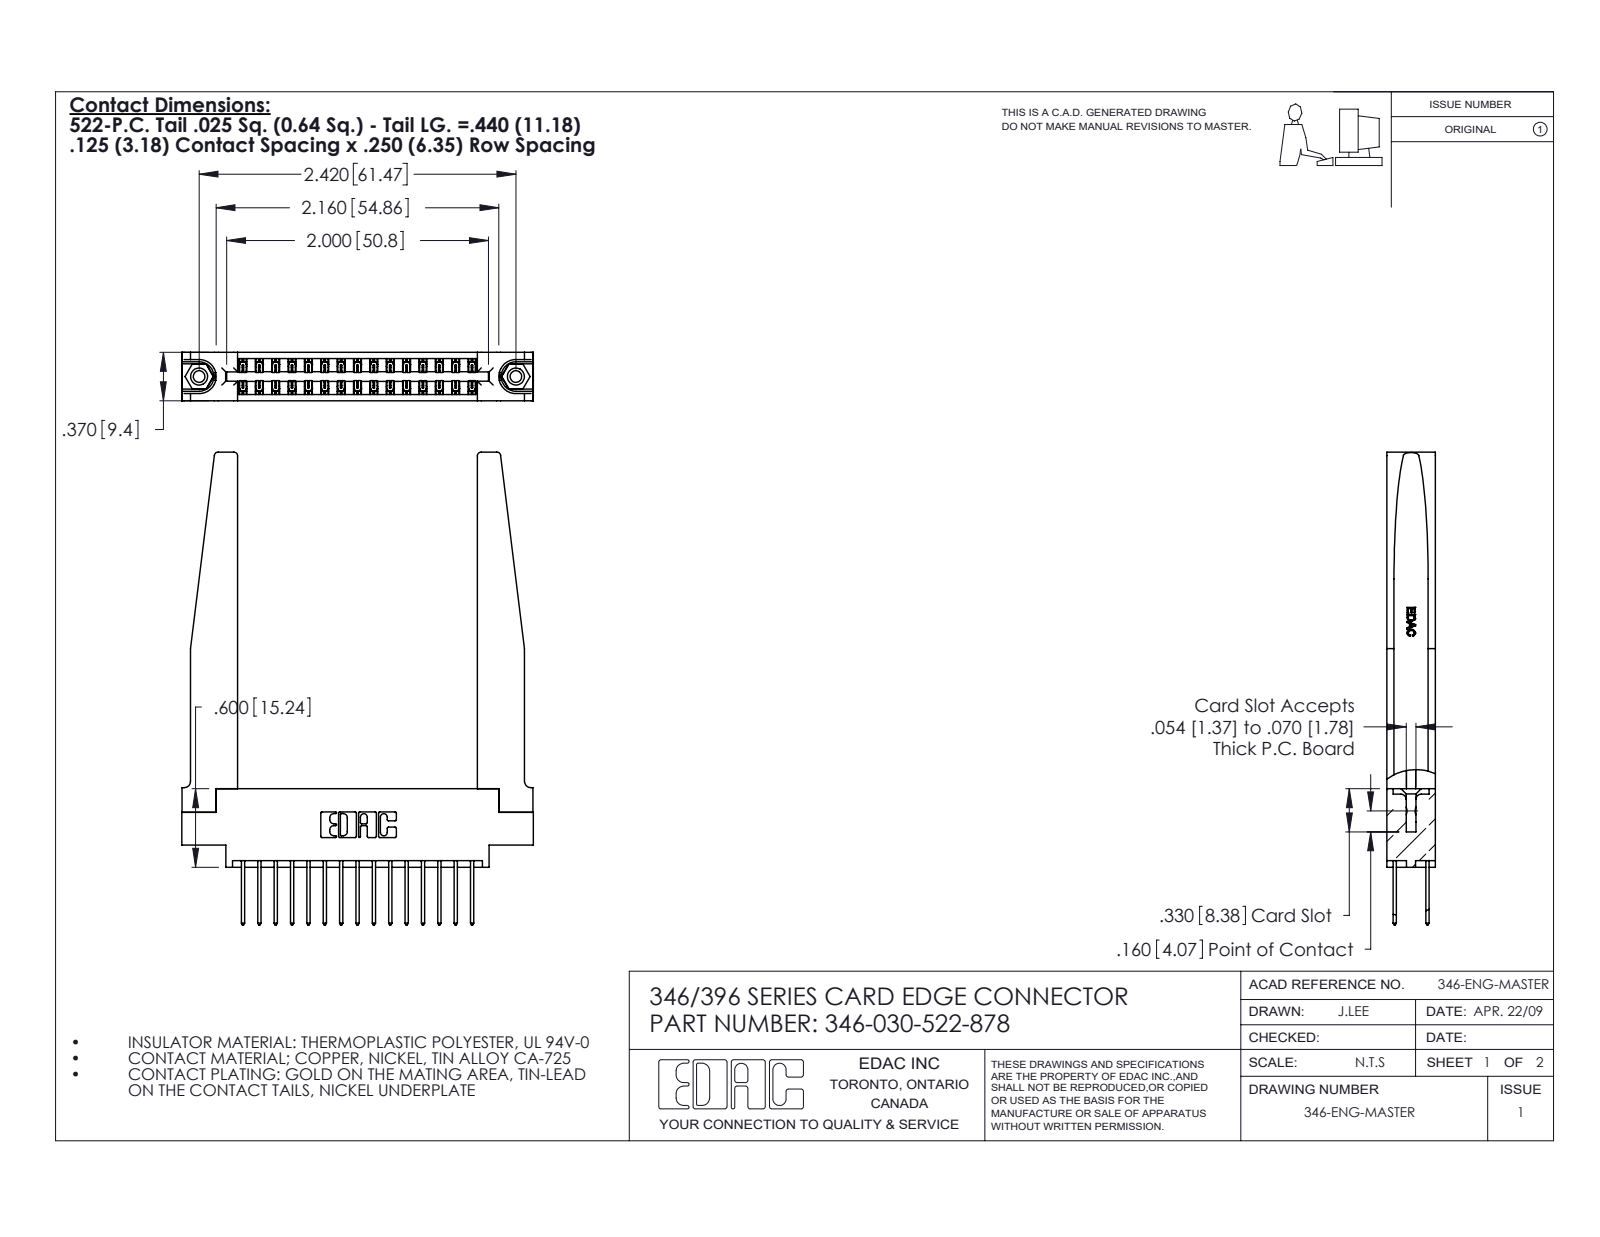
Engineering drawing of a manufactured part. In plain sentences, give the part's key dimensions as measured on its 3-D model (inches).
The part is named "345-292-001_345-293-122; 346-030-522-878; 345-250-001_345-250-001-102; 346-220-078_345-220-078 (+1 more)". Its 3-D file was written by "SolidWorks 2020 (CONFIG_CONTROL_DESIGN)". It is 35 solids with 1934 faces: 1286 planar, 596 cylindrical and 52 other. Overall it measures 3.61 by 2.685 by 0.37 inches. Its volume is 0.809 cubic inches and its surface area 23.88 square inches. Round holes: 2 of diameter 0.089, 2 of diameter 0.125, 2 of diameter 0.156, 1 of diameter 0.064. Round bosses or shafts: 2 of diameter 0.155. Partial cylindrical surfaces (rounded edges, fillets, slot ends): 45 of radius 0.006, 30 of radius 0.01, 22 of radius 0.01, 8 of radius 0.03, 6 of radius 0.007, 6 of radius 0.031, 3 of radius 0.026, 2 of radius 0.014. The main face-to-face distances are 0.37, 0.072, 0.048, 0.322, 0.148, 0.15, 0.25, 0.298, 0.025, 0.22. The hole center spacings are 0.246, 2.213, 2.42.
